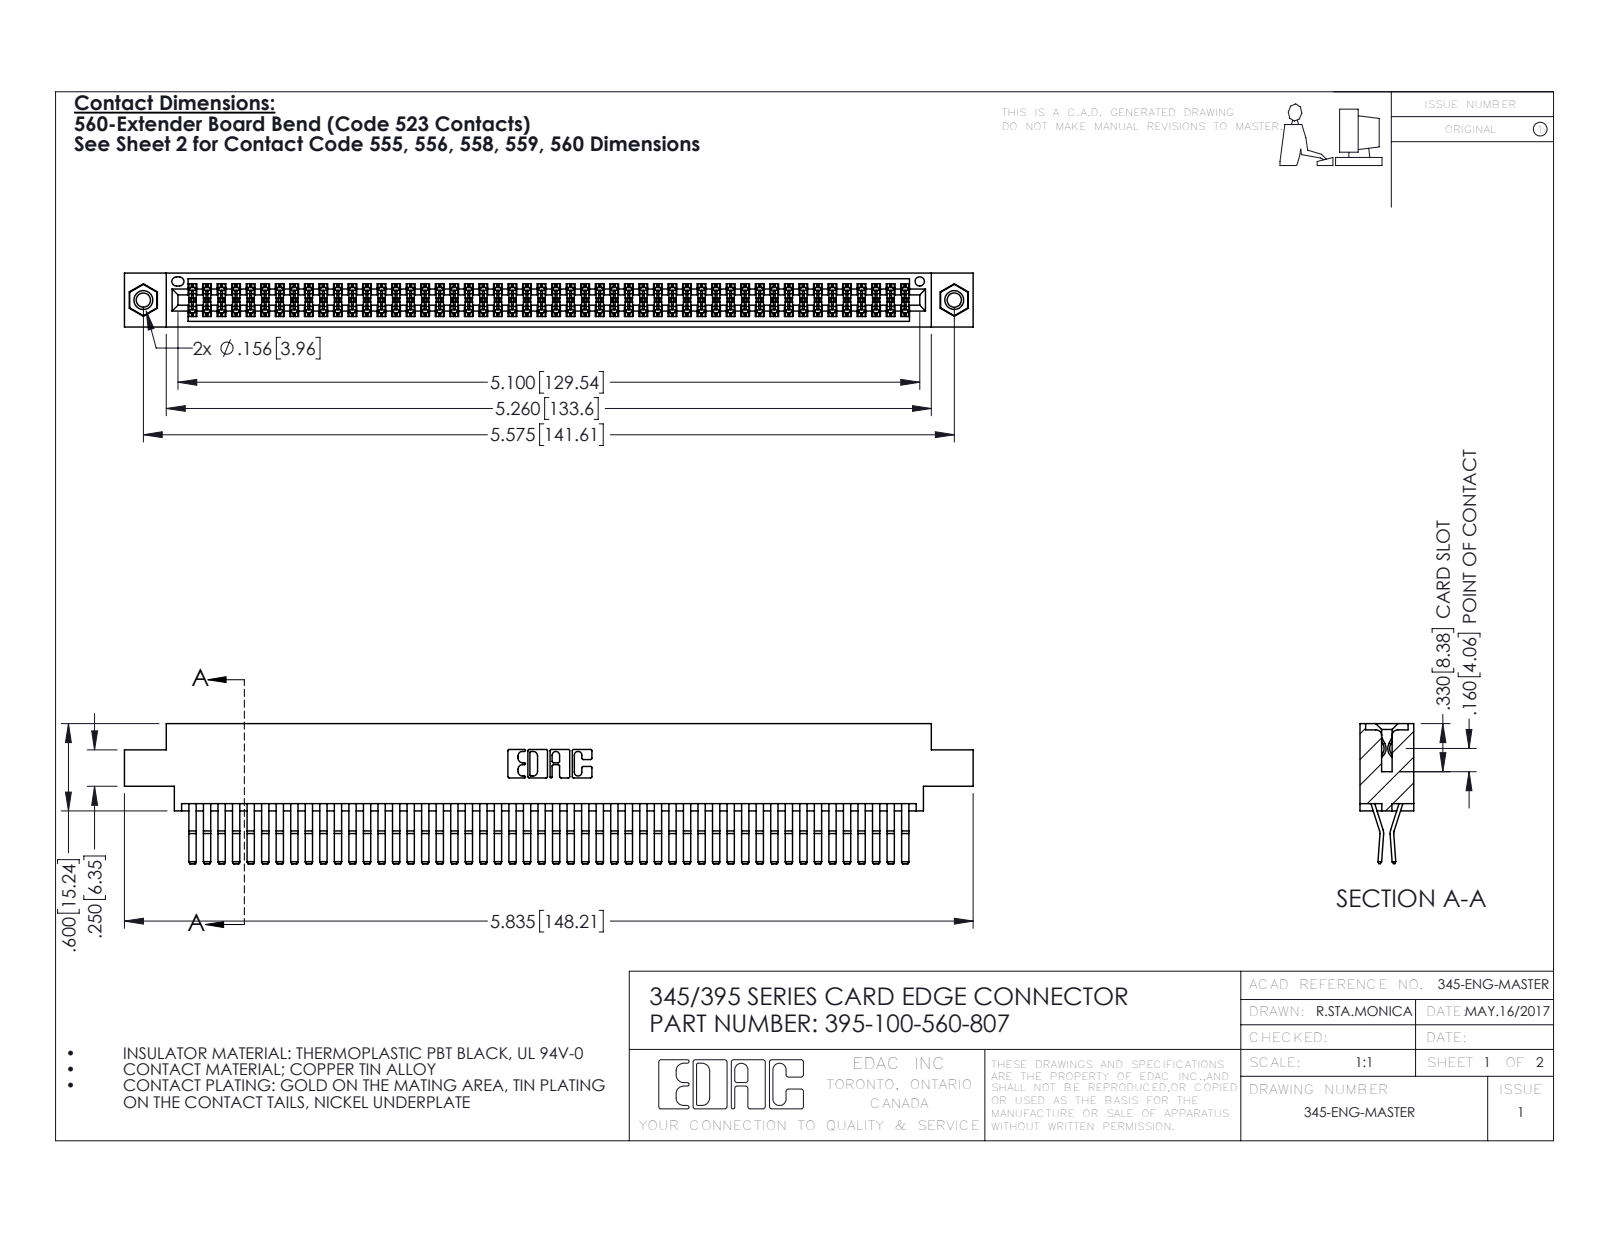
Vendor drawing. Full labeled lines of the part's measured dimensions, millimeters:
Part name (STEP PRODUCT): 395-100-560-807; 345 Part_0.170 Offset - 0.156 Dia-TI; 345-250-001_345-250-005-103; 345-292-001_560 Tail
STEP written by: SolidWorks 2016 (CONFIG_CONTROL_DESIGN)
Units: millimetres
Bodies: 103 solids, 5390 faces (3416 planar, 1958 cylindrical, 16 other)
Overall size (bounding box): 148.2 × 24.4 × 9.4
Volume: 15 000 mm³ · Surface area: 24 190 mm²
Round holes (diameter × count): ⌀2.5 ×2, ⌀3.2 ×2, ⌀4 ×2, ⌀1.6 ×1
Round bosses / shafts (diameter × count): ⌀3.9 ×2
Partial cylindrical surfaces — rounded edges, fillets, slot ends (radius × count): R0.2 ×151, R0.3 ×22, R0.2 ×6, R0.8 ×6, R0.7 ×3, R0.3 ×2, R0.4 ×2, R0.5 ×2
Main face-to-face distances: 0.6, 1.8, 7.6, 9.4, 5.1, 2.5, 6.9, 5.7, 4.4, 3.8
Hole centre spacings: 6.9, 135.6, 141.6
